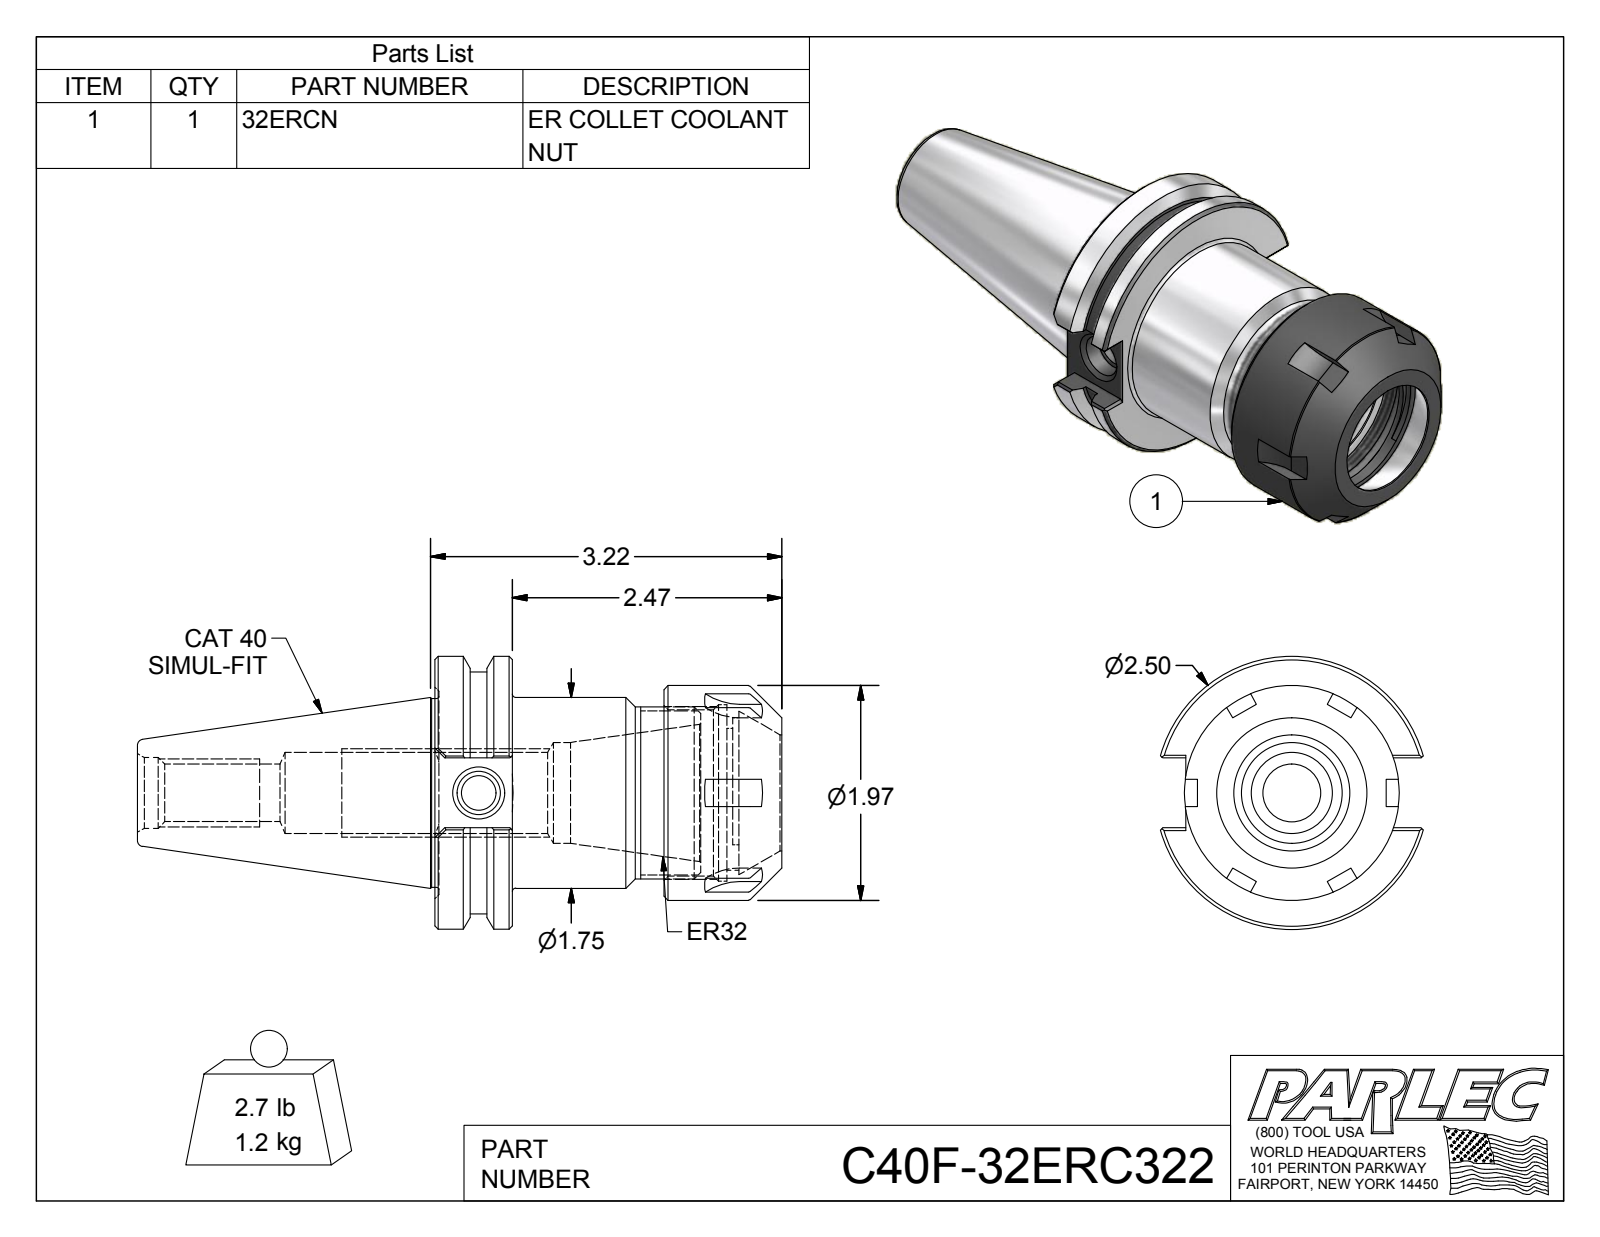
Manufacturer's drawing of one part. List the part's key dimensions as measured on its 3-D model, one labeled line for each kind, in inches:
Part name (STEP PRODUCT): C40F-32ERC322; C40F-32ER3-1; 32ERCN
STEP written by: Autodesk Inventor 2012 (AUTOMOTIVE_DESIGN)
Units: inches
Bodies: 2 solids, 121 faces (55 planar, 27 cylindrical, 39 other)
Overall size (bounding box): 5.908 × 2.5 × 2.406
Volume: 9.511 in³ · Surface area: 62.05 in²
Round holes (diameter × count): ⌀0.315 ×1, ⌀0.399 ×1, ⌀0.527 ×1, ⌀0.648 ×1, ⌀0.745 ×1, ⌀0.925 ×1, ⌀1.063 ×1, ⌀1.299 ×1, ⌀1.522 ×1, ⌀1.614 ×1
Round bosses / shafts (diameter × count): ⌀2.5 ×1, ⌀2.215 ×1, ⌀1.969 ×1, ⌀1.75 ×1, ⌀1.73 ×1, ⌀1.575 ×1
Partial cylindrical surfaces — rounded edges, fillets, slot ends (radius × count): R0.5 ×6, R0.689 ×1
Main face-to-face distances: 0.711, 2.098, 1.387, 2.677, 1.966, 0.579, 3.181, 2.47, 1.083, 0.504
Hole centre spacings: 0.059
